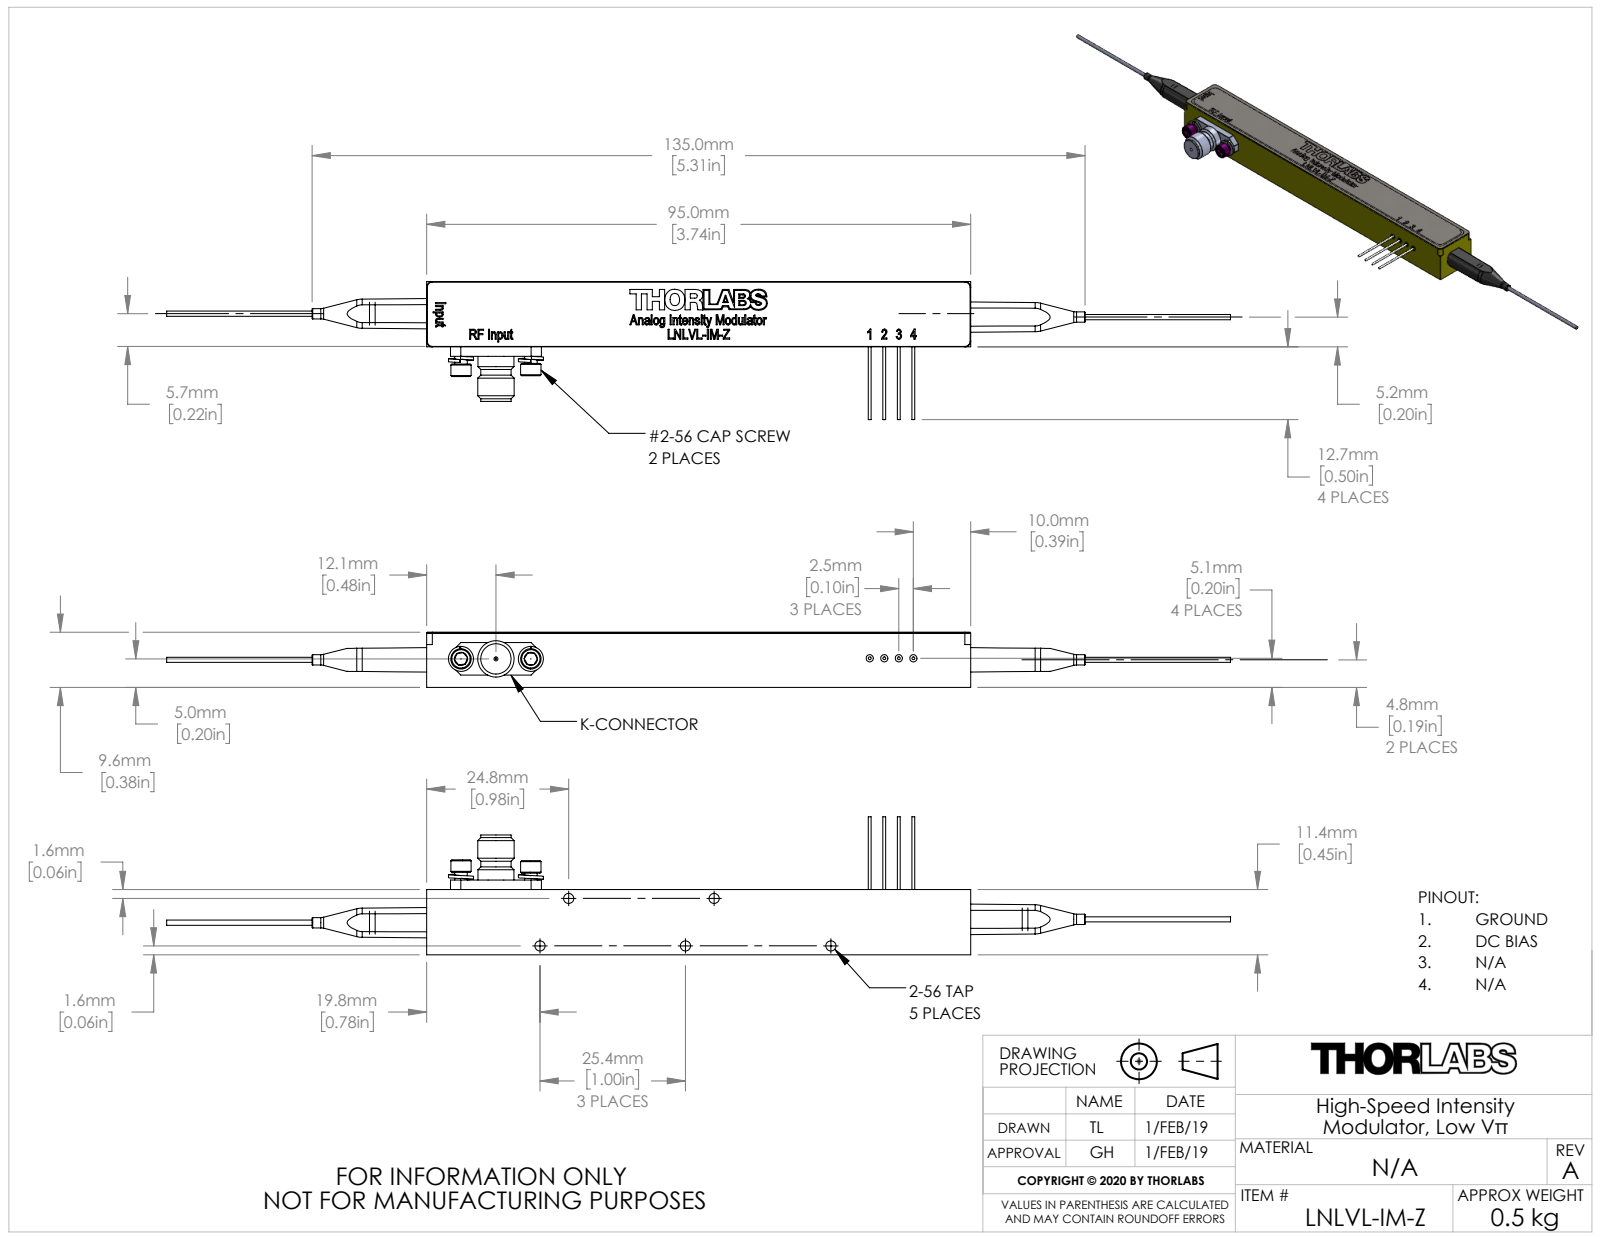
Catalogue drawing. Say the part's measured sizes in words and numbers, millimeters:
The part is named "QTN026069-E0W". Its 3-D file was written by "SolidWorks 2018 (CONFIG_CONTROL_DESIGN)". It is 0 solids with 376 faces: 246 planar, 34 cylindrical and 96 other. Overall it measures 185.78 by 24.1 by 9.64 millimeters. Round holes: 5 of diameter 1.78, 2 of diameter 1.27, 1 of diameter 0.7. Round bosses or shafts: 4 of diameter 0.51, 2 of diameter 3.56, 2 of diameter 2.18, 2 of diameter 1.8, 2 of diameter 0.9, 1 of diameter 6.35, 1 of diameter 6.3, 1 of diameter 5.3. Partial cylindrical surfaces (rounded edges, fillets, slot ends): 4 of radius 0.9, 4 of radius 1. The main face-to-face distances are 9.64, 11.4, 9.5, 95, 9.63, 11.3, 1.65, 13.05, 5.11, 5.1. The hole center spacings are 25.4, 9.67, 22.02, 2.54, 31.51, 46.54, 50.8, 67.82.
